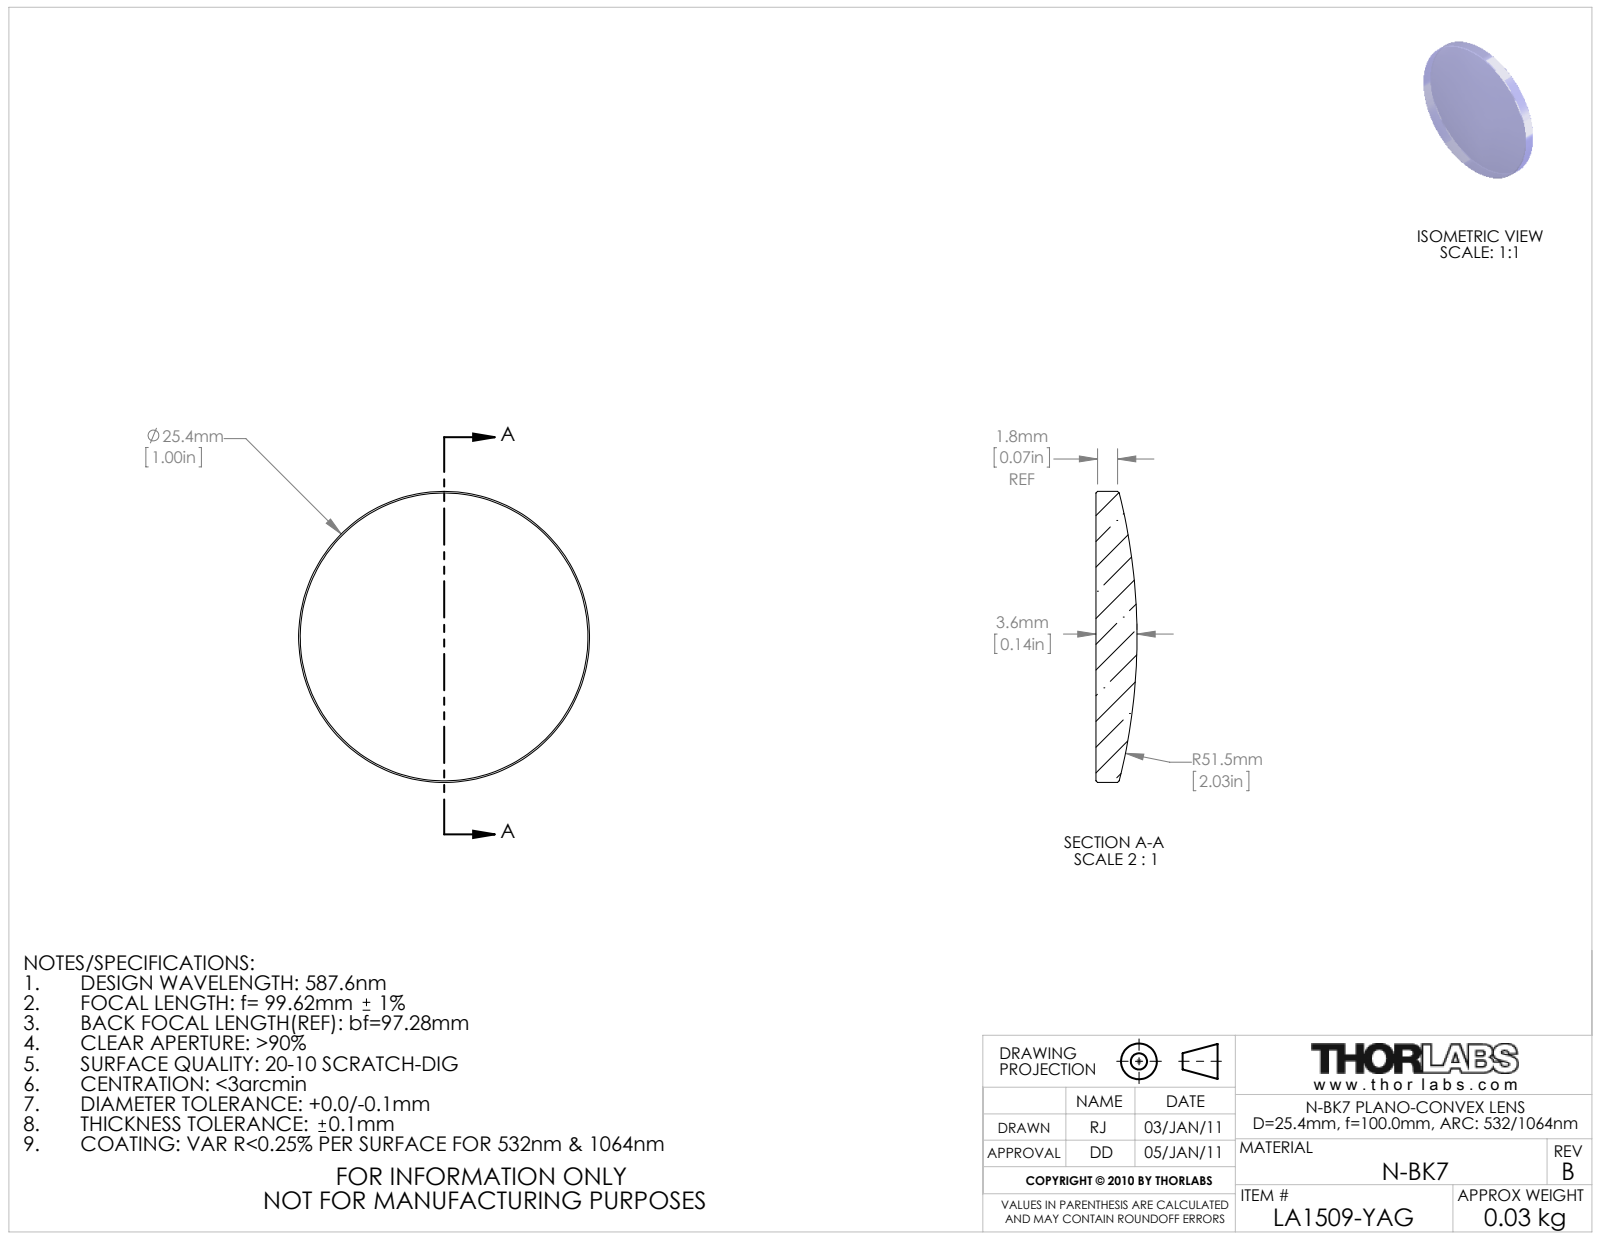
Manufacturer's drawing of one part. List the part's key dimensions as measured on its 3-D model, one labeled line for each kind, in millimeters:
Part name (STEP PRODUCT): 21791-E0W
STEP written by: SolidWorks 2011 (AUTOMOTIVE_DESIGN)
Units: millimetres
Bodies: 0 solids, 9 faces (1 planar, 2 cylindrical, 6 other)
Overall size (bounding box): 25.4 × 25.4 × 3.59
Round bosses / shafts (diameter × count): ⌀25.4 ×1
